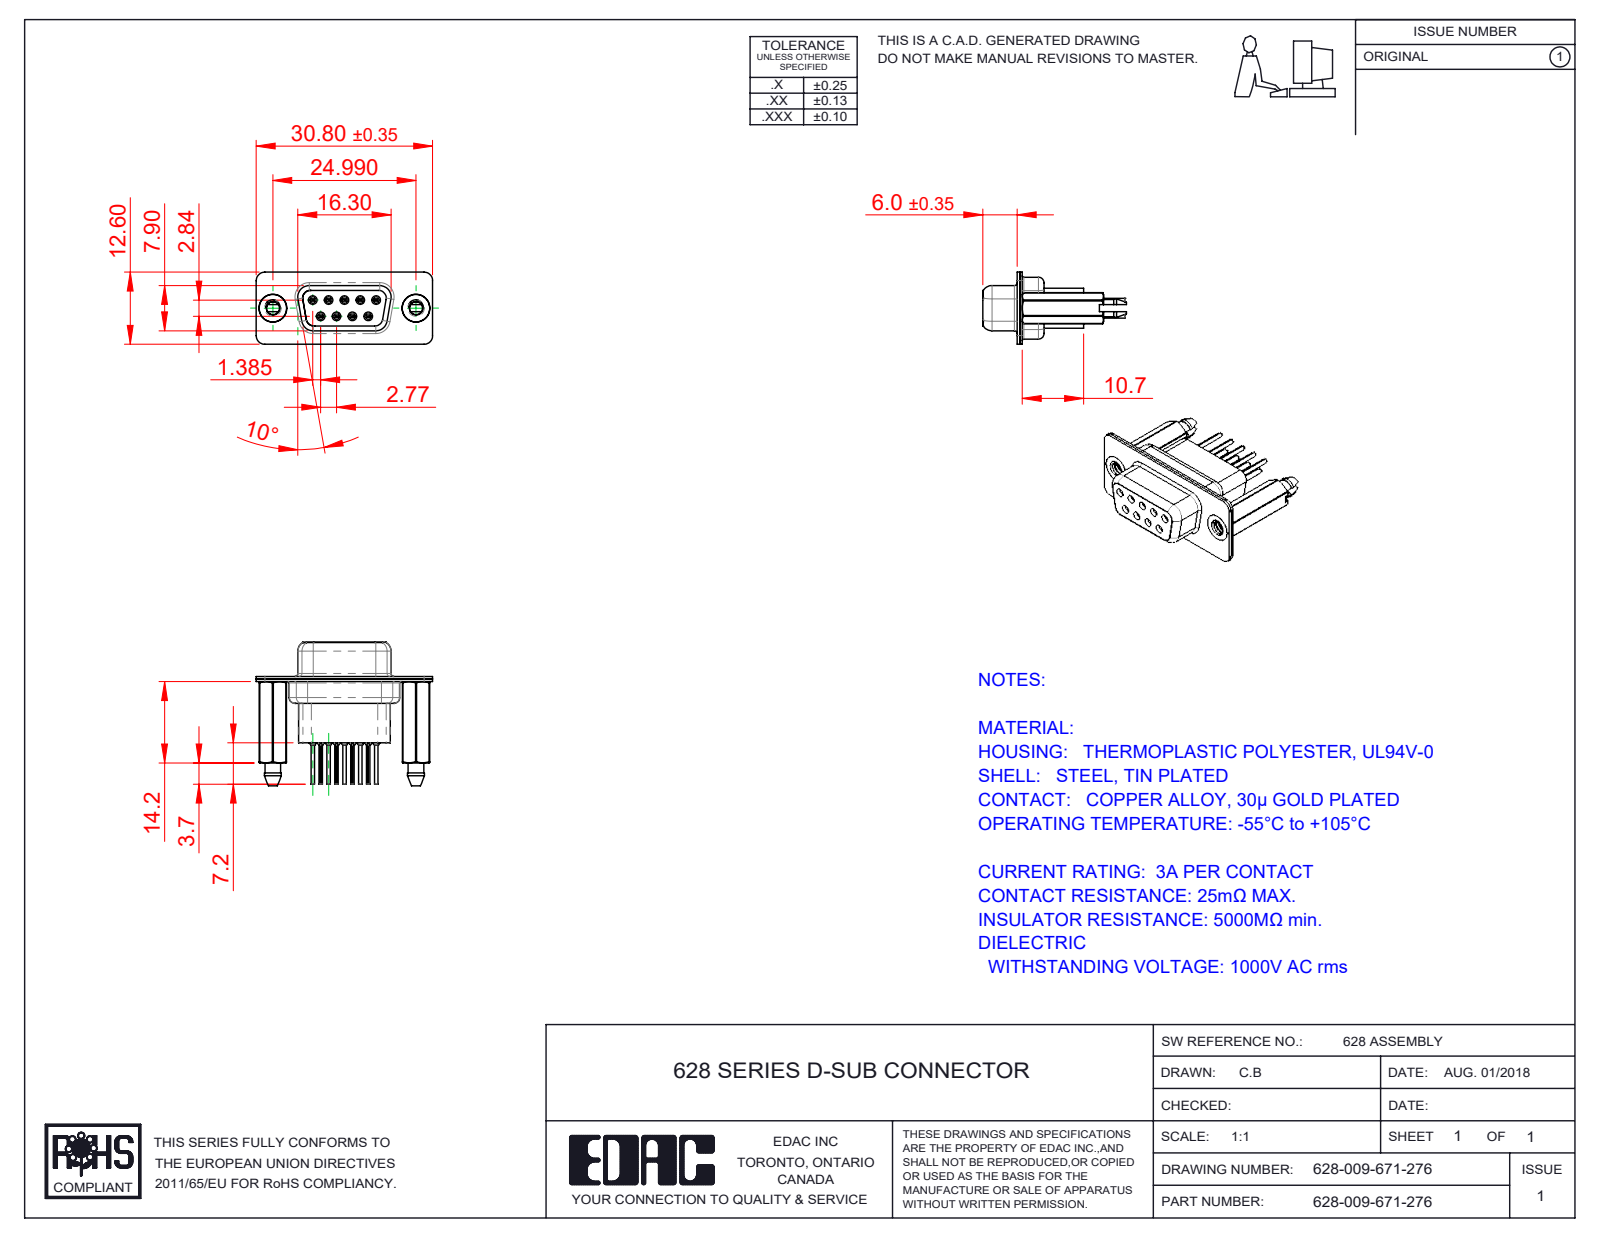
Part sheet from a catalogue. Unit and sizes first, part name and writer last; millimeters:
Units: millimetres
Overall size (bounding box): 30.8 × 25.1 × 12.6
Round holes (diameter × count): ⌀0.2 ×9, ⌀0.8 ×9, ⌀0.9 ×9, ⌀1.1 ×9, ⌀1.6 ×9, ⌀1.7 ×5, ⌀2.26 ×2, ⌀4 ×2, ⌀4.05 ×2, ⌀4.85 ×2
Round bosses / shafts (diameter × count): ⌀2 ×9, ⌀1.5 ×9, ⌀1.2 ×9, ⌀0.6 ×9, ⌀4.95 ×2, ⌀4.8 ×2
Partial cylindrical surfaces — rounded edges, fillets, slot ends (radius × count): R1.5 ×19, R0.1 ×18, R2 ×12, R0.28 ×9, R1.35 ×6, R1.6 ×6, R0.25 ×4, R0.5 ×4
Main face-to-face distances: 0.45, 0.4, 0.9, 8.5, 6.6, 1.9, 4.76, 1.4, 7, 10.7
Hole centre spacings: 3.16, 2.77, 5.54, 5.03, 5.04, 8.31, 7.48, 7.49
Volume: 2 610 mm³ · Surface area: 6 086 mm²
Bodies: 14 solids, 1460 faces (378 planar, 466 cylindrical, 616 other)
Part name (STEP PRODUCT): 628 Shell Front_09 Contacts; 628 Shell Rear_09 Contacts; 628 Housing_09 HP; 628 4-40 Threaded Boardlock_HP71 (+3 more)
STEP written by: SolidWorks 2020 (CONFIG_CONTROL_DESIGN)
